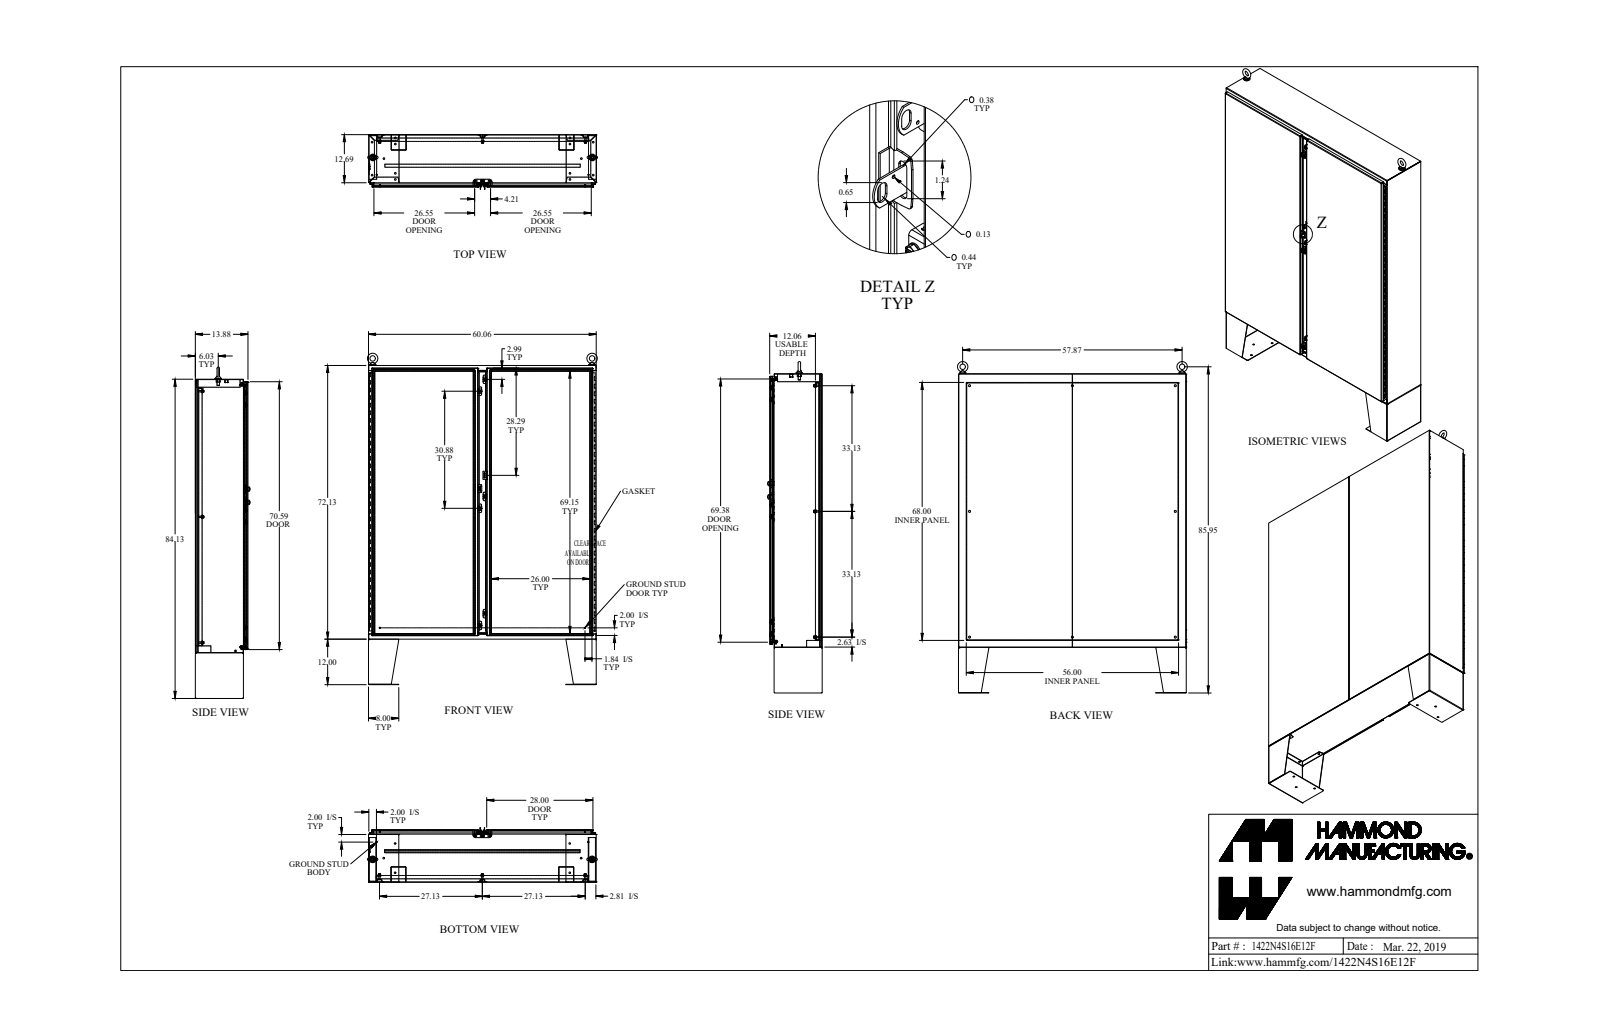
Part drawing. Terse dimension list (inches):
name: 1422N4S16E12F_Default
written by: SolidWorks 2019 (CONFIG_CONTROL_DESIGN)
unit: in
bodies: 110 solids, 3487 faces (1684 planar, 1583 cylindrical, 220 other)
size: 87.784 × 61.121 × 14.438
volume: 1 964 in³; area: 39 803 in²
holes: 24× ⌀0.304, 14× ⌀0.437, 8× ⌀0.307, 8× ⌀0.445, 8× ⌀0.563, 6× ⌀0.213, 6× ⌀0.265, 6× ⌀0.375, 3× ⌀0.201, 3× ⌀0.25, 3× ⌀0.313, 2× ⌀0.11
bosses: 8× ⌀1, 8× ⌀0.65, 8× ⌀0.375, 8× ⌀0.332, 6× ⌀0.5, 6× ⌀0.39, 6× ⌀0.244, 4× ⌀0.313
rounds: 69× R0.048, 69× R0.143, 34× R0.25, 18× R0.06, 12× R0.116, 12× R0.141, 10× R0.125, 8× R0.05
face distances: 0.095, 13.78, 13.685, 13.875, 0.125, 11.998, 12.093, 1.687, 1.782, 12.218
hole spacings: 6, 58.491, 12, 18, 24, 30, 36, 58.183
